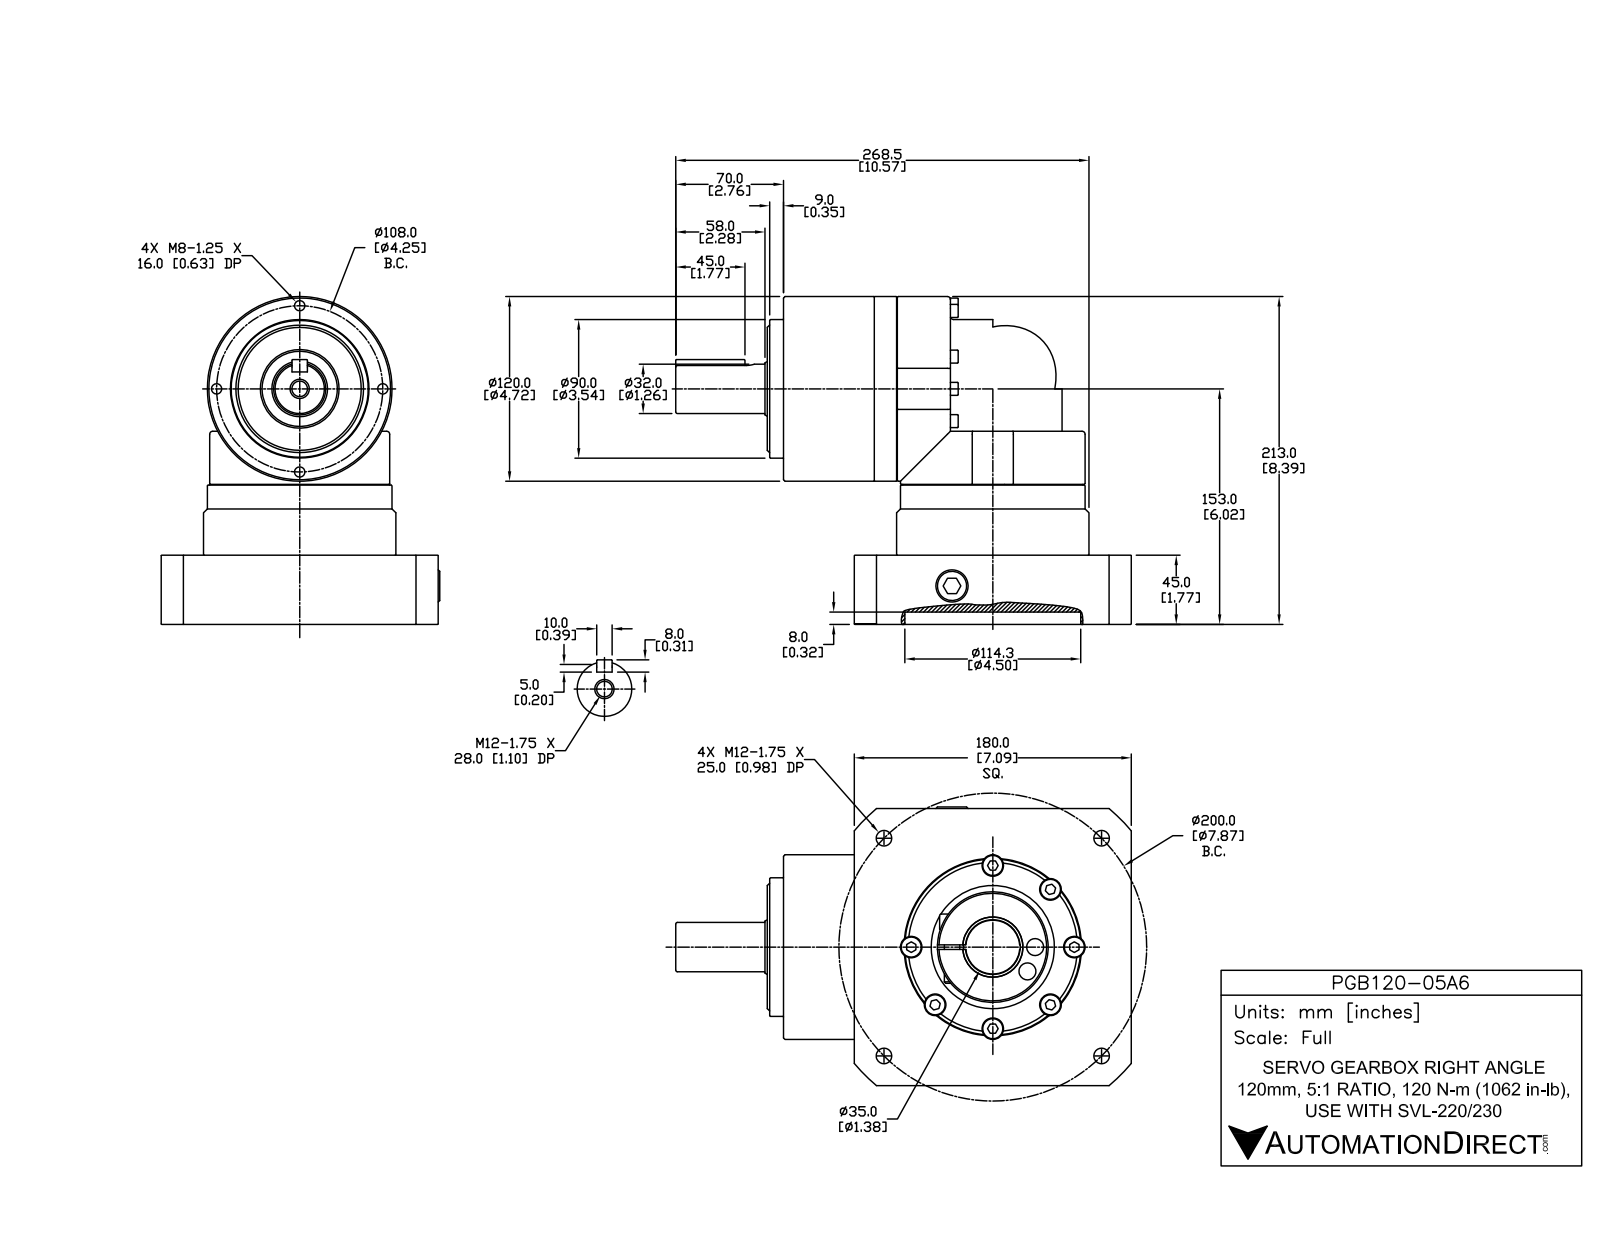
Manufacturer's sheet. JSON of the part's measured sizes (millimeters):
{"part_name": "PGB120-05A6", "step_written_by": "SolidWorks 2014 (AUTOMOTIVE_DESIGN)", "units": "millimeters", "bodies": {"solids": 1, "faces": 580, "planar": 245, "cylindrical": 150, "other": 185}, "overall_size": [296, 213, 181], "volume_mm3": 3608000, "surface_area_mm2": 243000, "round_holes": [[14, 7], [10.1, 5], [6.7, 4], [11, 3], [17.5, 1], [35, 1], [80, 1]], "round_bosses_or_shafts": [[8.5, 9], [13, 7], [120, 2], [117, 2], [125, 1], [90, 1], [72, 1], [39, 1]], "partial_cylinders_radius": [[2, 6], [2.5, 2], [4.2, 1], [5, 1], [45, 1], [55, 1], [57.2, 1], [117.5, 1]], "face_to_face_distances": [45, 180, 46, 9, 226, 36, 56.5, 236.5, 10.5, 148.5], "hole_center_spacings": [72.9, 142.5, 53, 40.6, 97.9, 113.2, 54, 75]}
